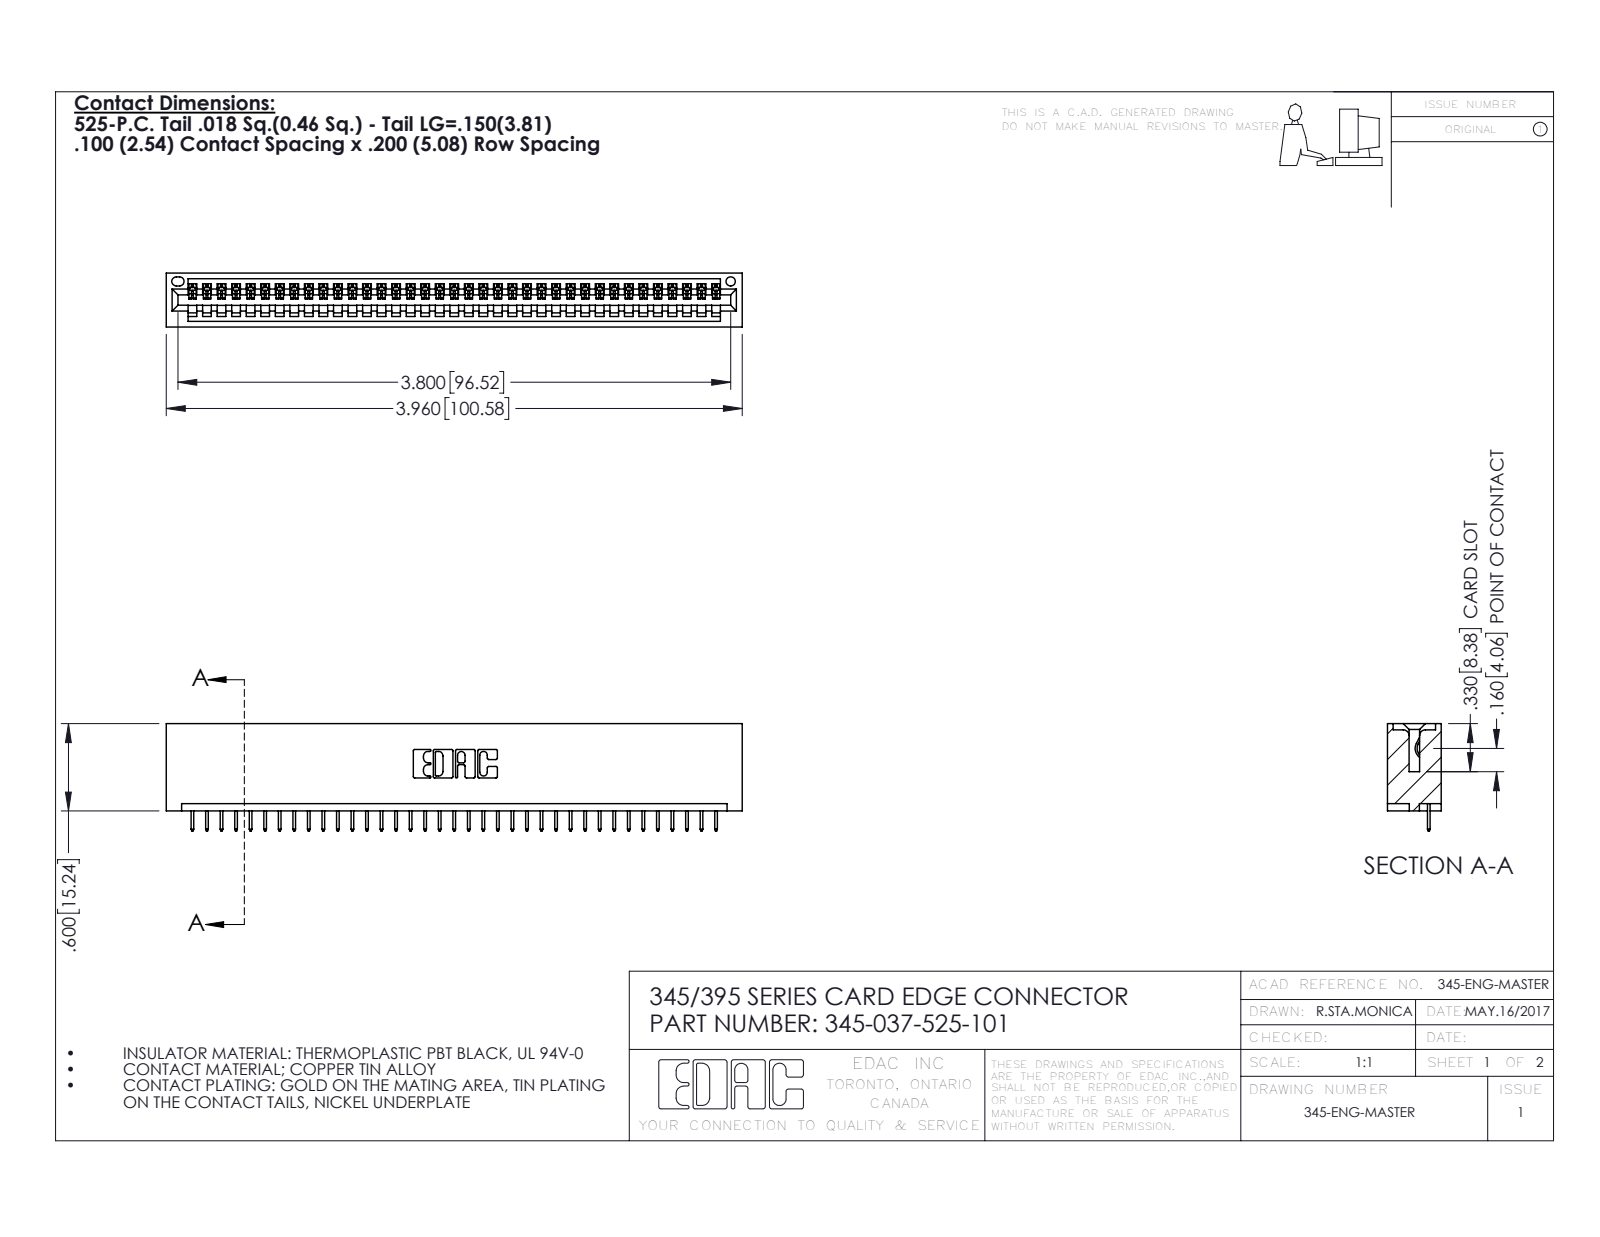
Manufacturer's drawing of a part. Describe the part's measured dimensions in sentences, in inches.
The part is named "345 Part_No Mounting Lugs; 345-292-001_345-293-125; 345-037-525-101". Its 3-D file was written by "SolidWorks 2020 (CONFIG_CONTROL_DESIGN)". It is 38 solids with 2412 faces: 1778 planar, 634 cylindrical and 0 other. Overall it measures 3.96 by 0.737 by 0.37 inches. Its volume is 0.607 cubic inches and its surface area 19.9 square inches. Round holes: 1 of diameter 0.064. Partial cylindrical surfaces (rounded edges, fillets, slot ends): 74 of radius 0.006, 22 of radius 0.01, 6 of radius 0.007, 6 of radius 0.031, 3 of radius 0.026, 2 of radius 0.031, 2 of radius 0.04, 1 of radius 0.014. The main face-to-face distances are 0.298, 0.072, 0.37, 0.2, 0.098, 0.272, 0.025, 0.225, 0.072, 0.149.
